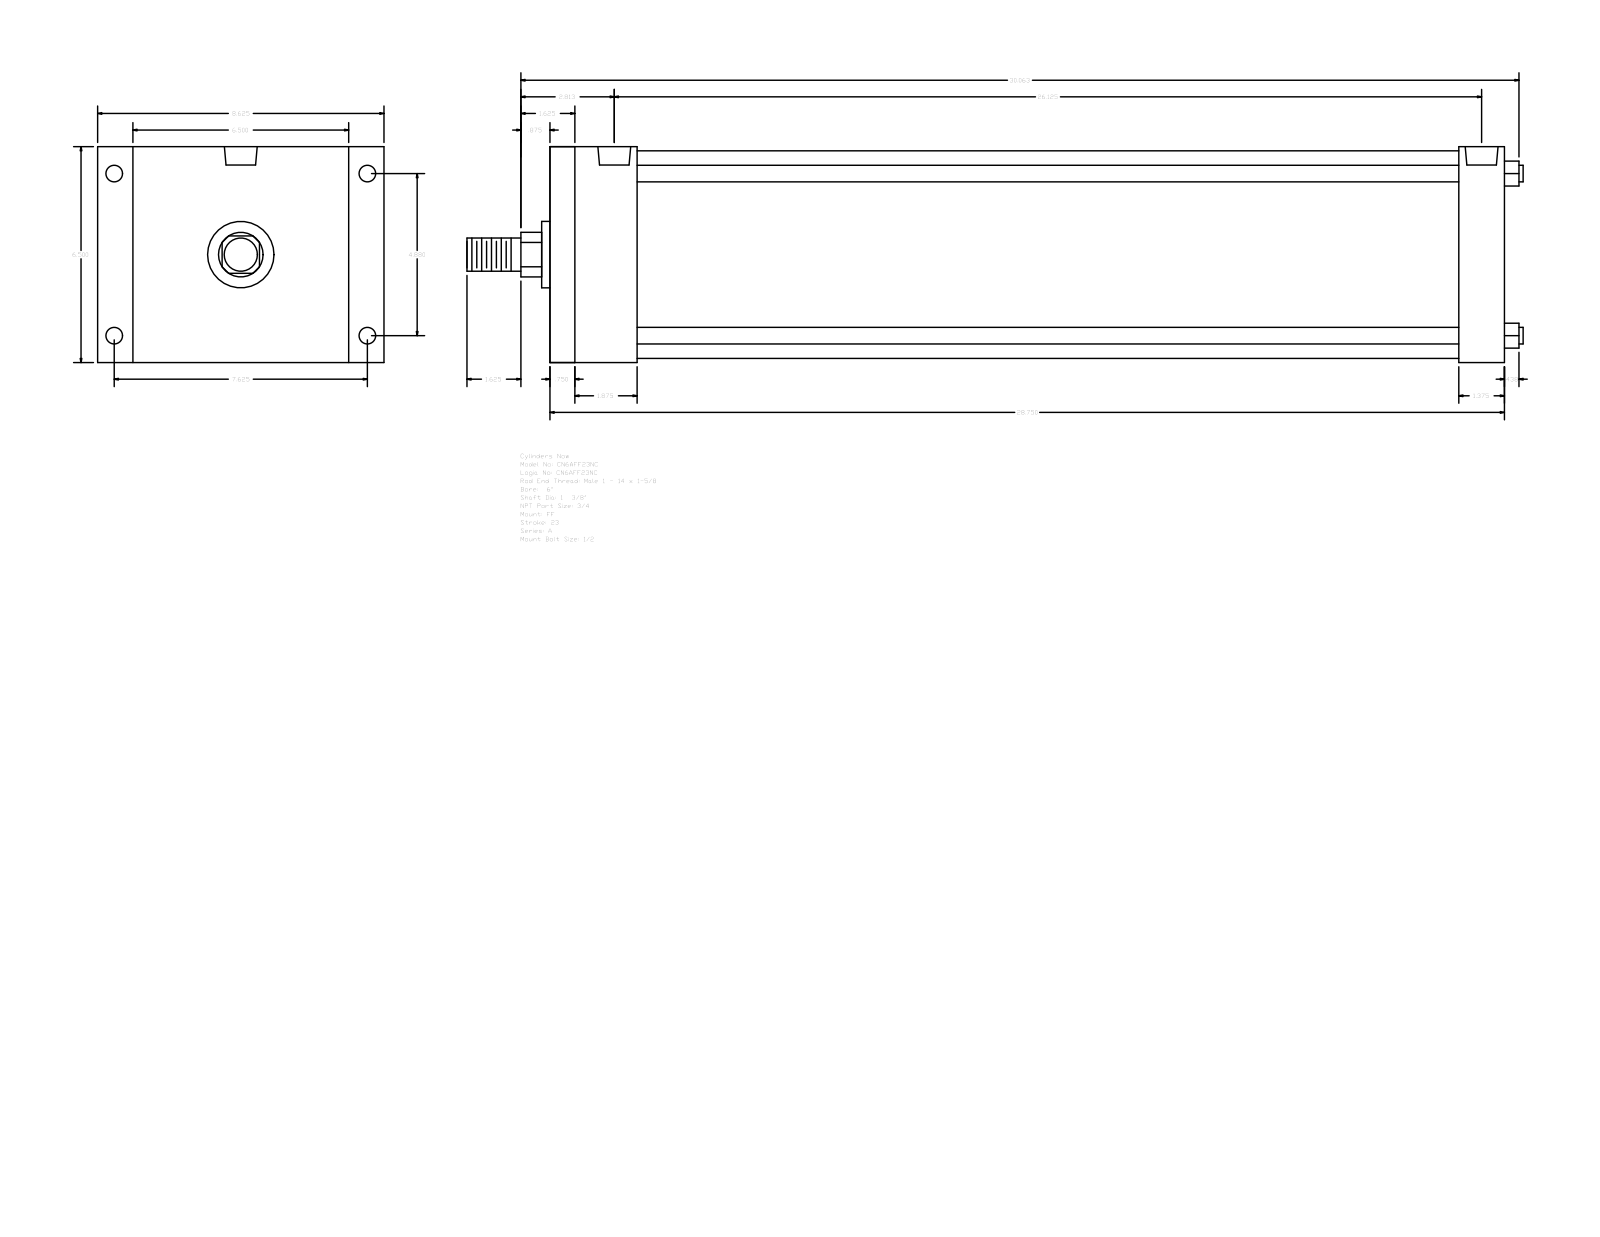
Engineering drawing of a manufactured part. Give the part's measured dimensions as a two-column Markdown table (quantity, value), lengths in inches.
| quantity | value |
| --- | --- |
| part name | A_FF__0600_1.375 |
| STEP written by | GSSL Pune (CONFIG_CONTROL_DESIGN) |
| units | inches |
| bodies | 0 solids, 92 faces (64 planar, 28 cylindrical, 0 other) |
| overall size | 31.813 × 8.625 × 6.5 |
| round holes (diameter × count) | 0.5 × 4, 0.594 × 4, 0.989 × 2 |
| round bosses / shafts (diameter × count) | 0.5 × 4, 6.25 × 1, 2 × 1, 1.375 × 1, 1 × 1 |
| partial cylindrical surfaces (radius × count) | 0.672 × 1 |
| main face-to-face distances | 6.5, 28.75, 0.75, 28, 2.625, 1.875, 26.125, 27.375, 26.625, 24.75 |
| hole center spacings | 0.219, 4.88, 7.625, 9.053, 25.687, 25.906, 26.125 |
